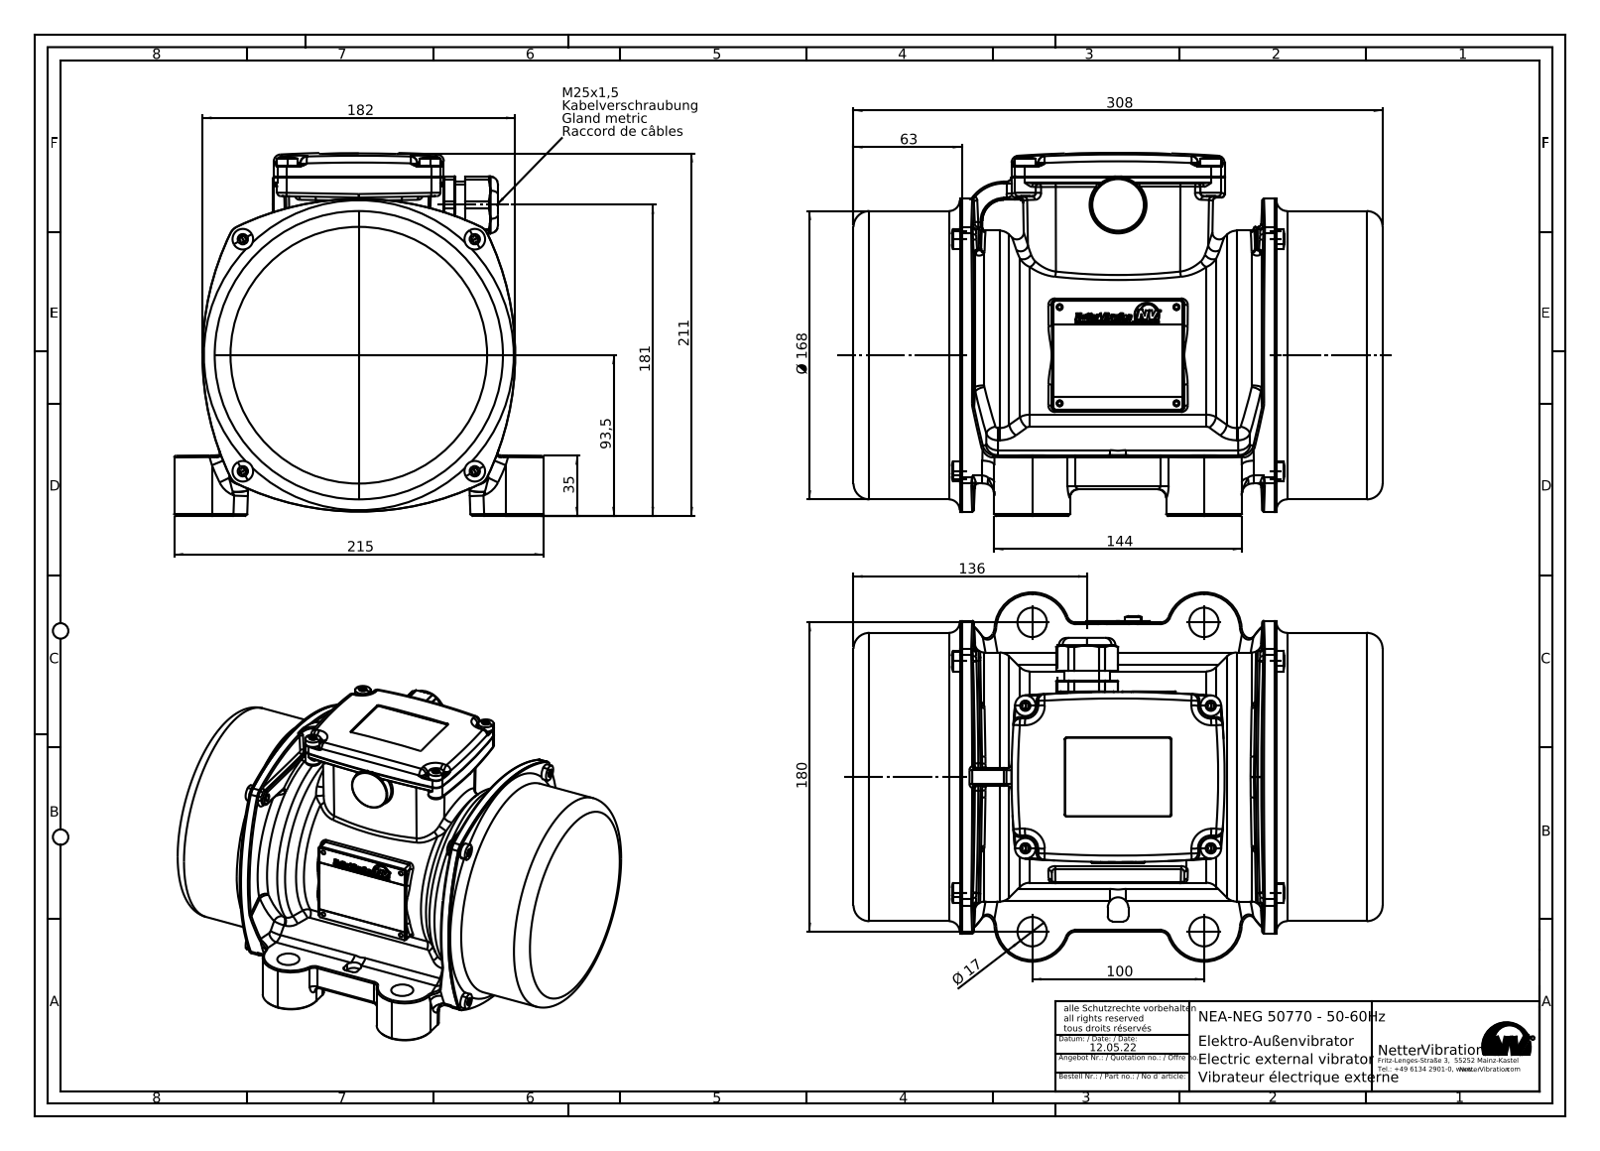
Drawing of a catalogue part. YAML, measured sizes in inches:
part_name: "NEA-NEG 50770-50-60Hz"
step_written_by: "SolidWorks 2015 (AUTOMOTIVE_DESIGN)"
units: inches
bodies: {solids: 23, faces: 3225, planar: 927, cylindrical: 728, other: 1570}
overall_size: [12.126, 8.465, 8.315]
volume: 94.16
surface_area: 979.7
round_holes:
  - {diameter: 0.134, count: 4}
  - {diameter: 0.177, count: 4}
  - {diameter: 0.256, count: 4}
  - {diameter: 0.354, count: 4}
  - {diameter: 0.63, count: 2}
  - {diameter: 0.433, count: 1}
  - {diameter: 0.728, count: 1}
  - {diameter: 0.925, count: 1}
  - {diameter: 4.346, count: 1}
  - {diameter: 5.118, count: 1}
  - {diameter: 6.512, count: 1}
  - {diameter: 6.949, count: 1}
round_bosses_or_shafts:
  - {diameter: 0.472, count: 8}
  - {diameter: 0.236, count: 8}
  - {diameter: 0.394, count: 2}
  - {diameter: 0.197, count: 2}
  - {diameter: 6.606, count: 1}
  - {diameter: 6.496, count: 1}
  - {diameter: 6.488, count: 1}
  - {diameter: 5.709, count: 1}
partial_cylinders:
  - {radius: 0.039, count: 30}
  - {radius: 0.02, count: 28}
  - {radius: 0.079, count: 26}
  - {radius: 0.012, count: 20}
  - {radius: 0.197, count: 20}
  - {radius: 0.394, count: 16}
  - {radius: 0.118, count: 14}
  - {radius: 0.315, count: 14}
face_to_face_distances: [0.047, 12.079, 2.433, 9.646, 12.126, 12.031, 0.354, 2.126, 10, 2.079]
hole_center_spacings: [3.76, 5.317, 1.874, 2.205, 2.326, 2.677, 3.268, 3.468]
